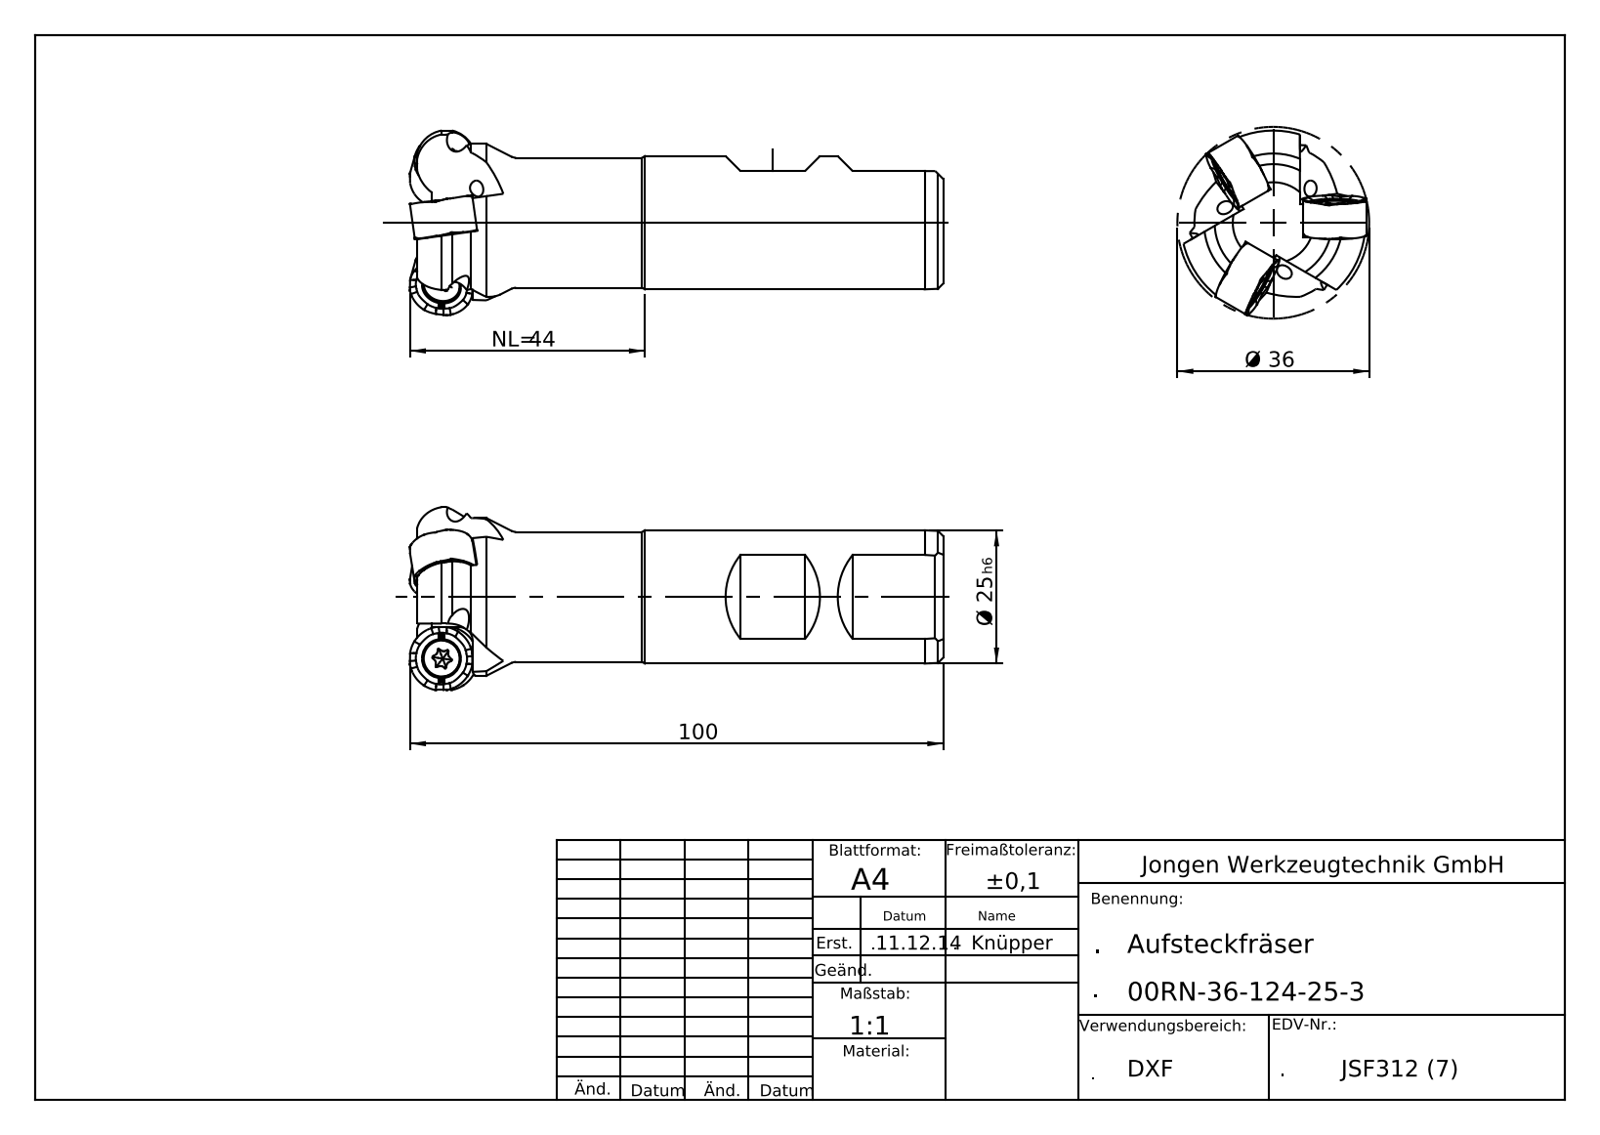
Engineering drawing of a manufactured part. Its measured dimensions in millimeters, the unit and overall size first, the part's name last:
Units: millimetres
Overall size (bounding box): 99.99 × 35.96 × 35.96
Round holes (diameter × count): ⌀3 ×3, ⌀6.5 ×1
Round bosses / shafts (diameter × count): ⌀25 ×1, ⌀24.4 ×1
Partial cylindrical surfaces — rounded edges, fillets, slot ends (radius × count): R2.15 ×3, R2.5 ×3, R4.5 ×3, R6 ×3, R14.8 ×1
Main face-to-face distances: 96.05, 14.89, 6.2, 10.95, 25.84, 0.6, 5.6, 0.67
Volume: 48 824 mm³ · Surface area: 12 455 mm²
Bodies: 1 solid, 95 faces (41 planar, 30 cylindrical, 24 other)
Part name (STEP PRODUCT): 00RN_36_124_25_3
STEP written by: SolidWorks 2016 (AUTOMOTIVE_DESIGN)
